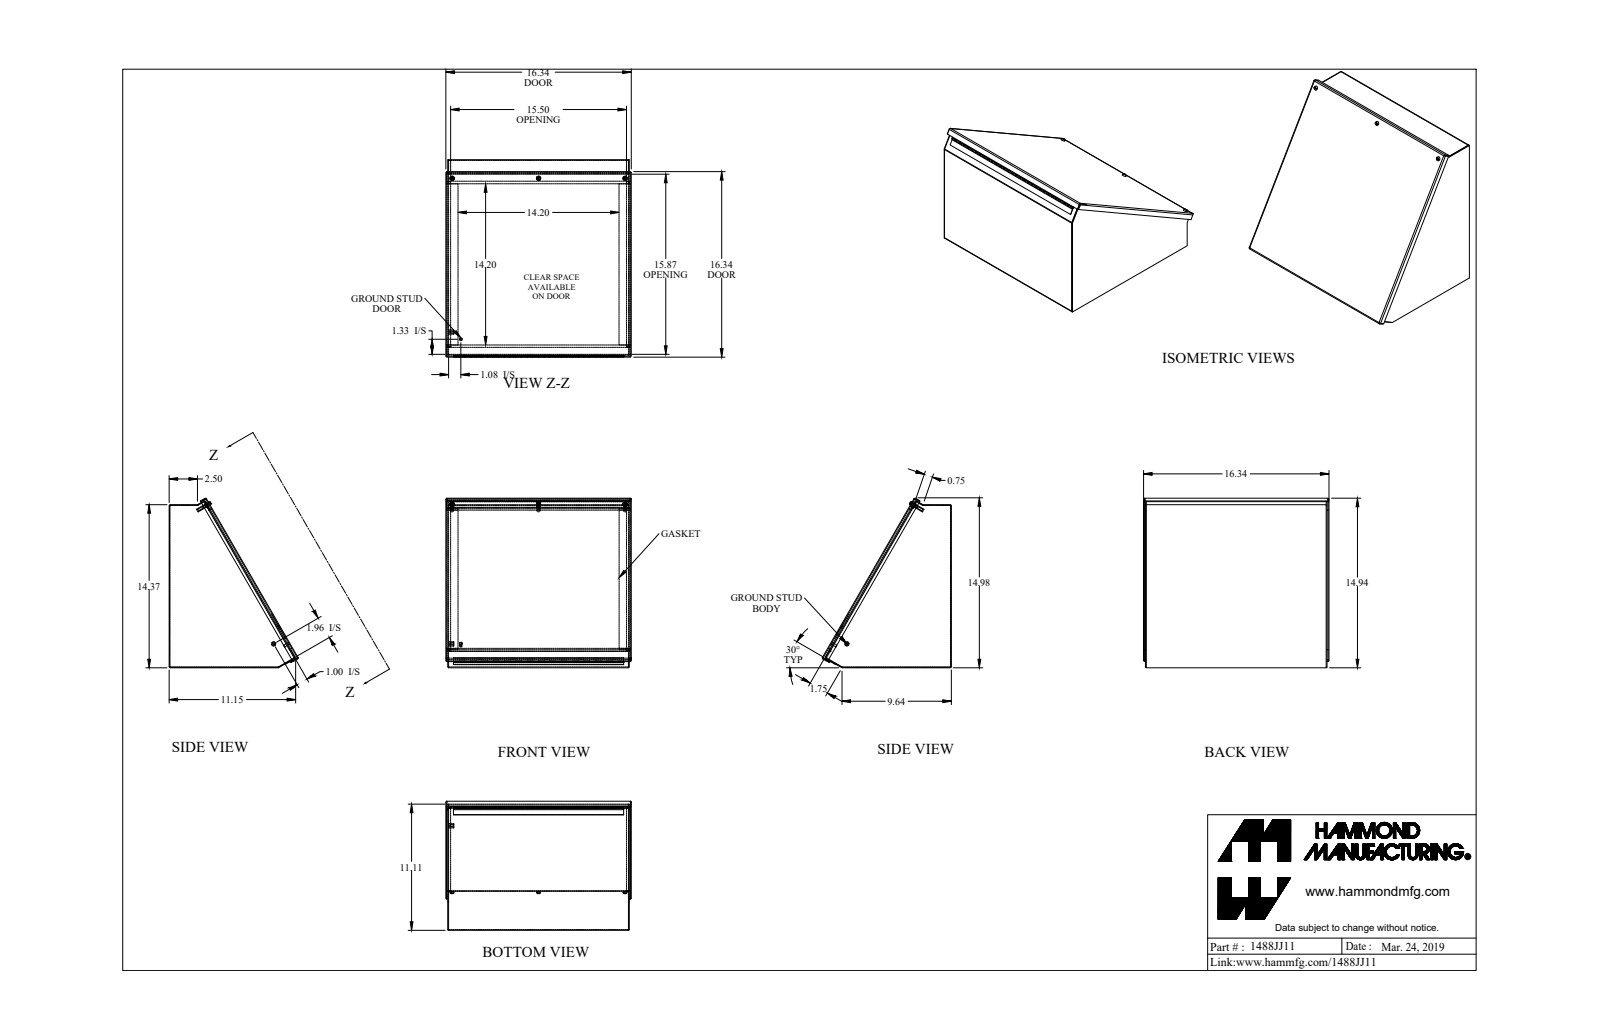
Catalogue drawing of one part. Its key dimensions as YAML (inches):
part_name: "1488JJ11_Default"
step_written_by: "SolidWorks 2019 (CONFIG_CONTROL_DESIGN)"
units: inches
bodies: {solids: 22, faces: 638, planar: 381, cylindrical: 221, other: 36}
overall_size: [16.343, 14.936, 11.372]
volume: 87.38
surface_area: 2205
round_holes:
  - {diameter: 0.159, count: 3}
  - {diameter: 0.25, count: 3}
  - {diameter: 0.156, count: 1}
round_bosses_or_shafts:
  - {diameter: 0.39, count: 3}
  - {diameter: 0.275, count: 3}
  - {diameter: 0.19, count: 3}
  - {diameter: 0.148, count: 3}
  - {diameter: 0.375, count: 1}
  - {diameter: 0.25, count: 1}
  - {diameter: 0.188, count: 1}
  - {diameter: 0.1, count: 1}
partial_cylinders:
  - {radius: 0.036, count: 12}
  - {radius: 0.108, count: 12}
  - {radius: 0.125, count: 3}
  - {radius: 0.16, count: 3}
  - {radius: 0.171, count: 3}
  - {radius: 0.025, count: 2}
  - {radius: 0.055, count: 1}
  - {radius: 0.057, count: 1}
face_to_face_distances: [0.072, 15.928, 15.856, 16, 14.293, 0.25, 0.322, 14.365, 14.221, 0.172]
hole_center_spacings: [7.625, 7.625, 15.25, 15.25]
